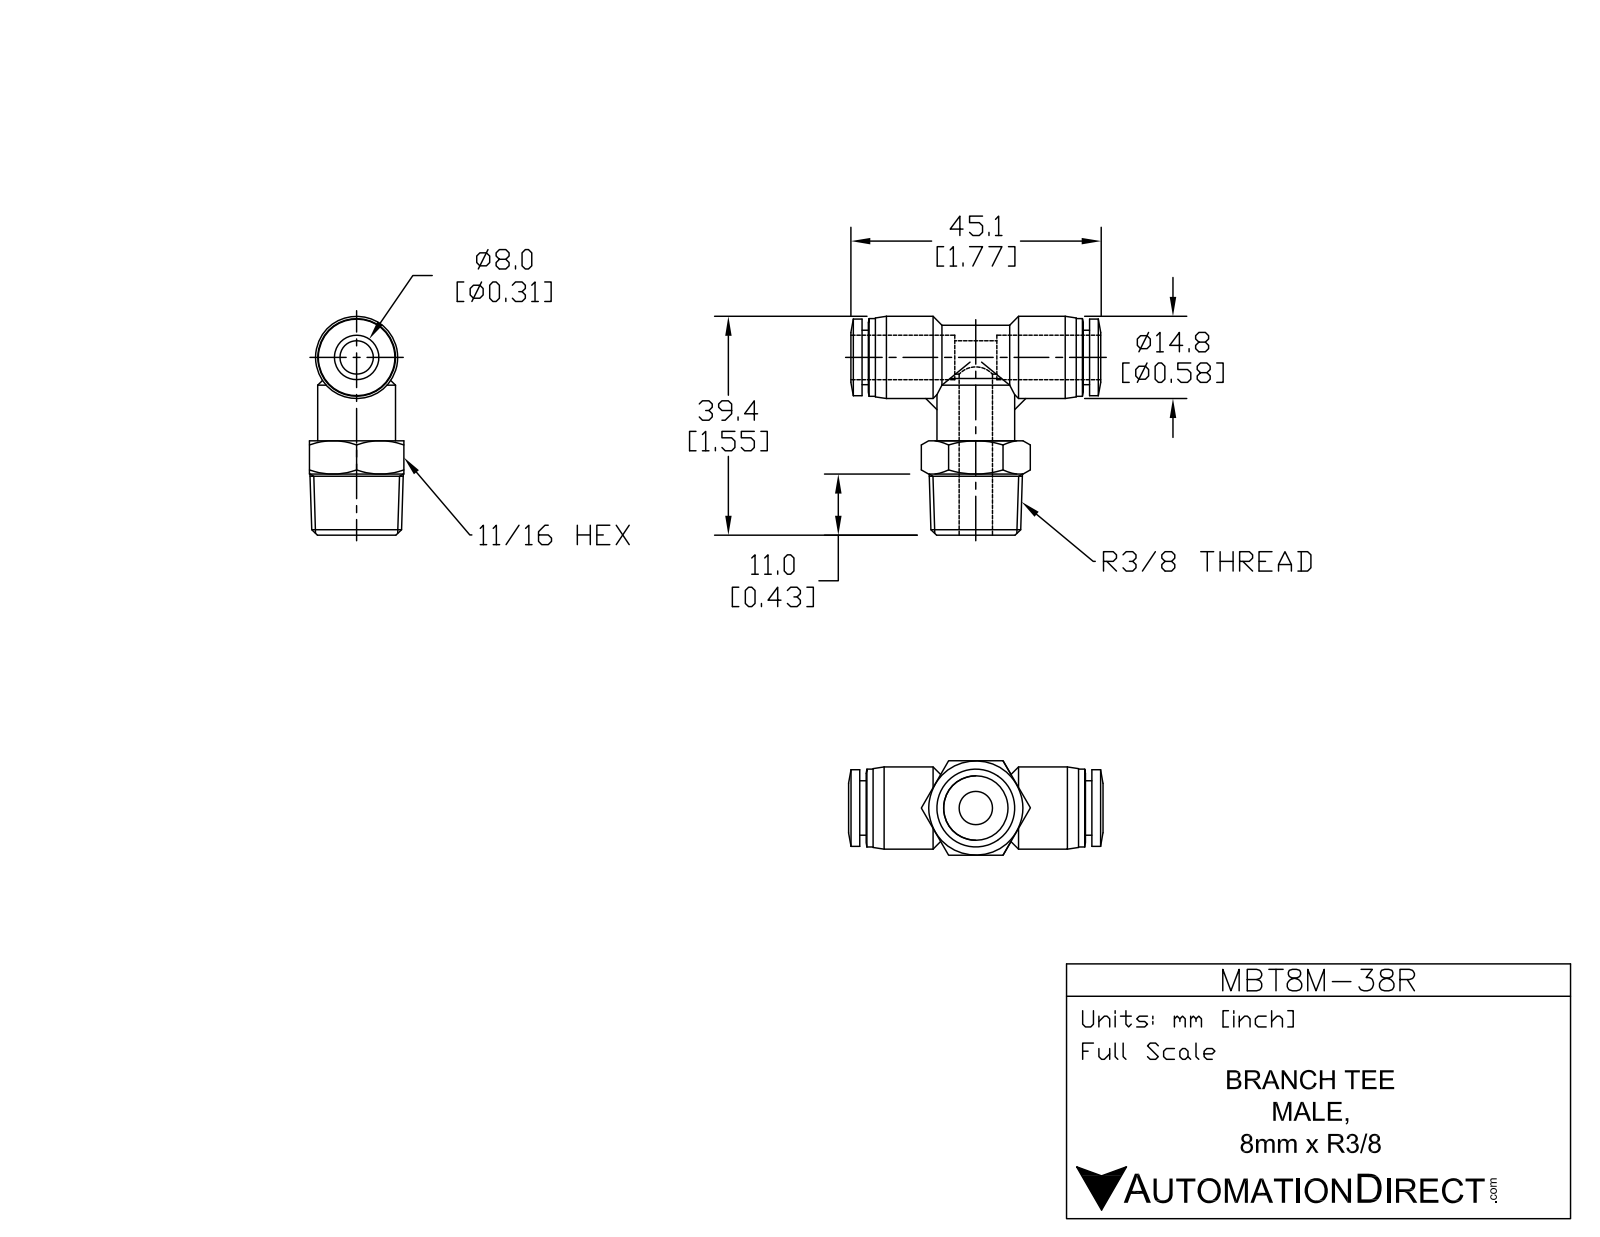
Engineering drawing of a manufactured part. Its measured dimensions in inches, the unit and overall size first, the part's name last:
Units: inches
Overall size (bounding box): 1.78 × 1.555 × 0.669
Round holes (diameter × count): ⌀0.236 ×2, ⌀0.327 ×1
Round bosses / shafts (diameter × count): ⌀0.591 ×1, ⌀0.559 ×1, ⌀0.551 ×1, ⌀0.543 ×1, ⌀0.457 ×1, ⌀0.386 ×1
Partial cylindrical surfaces — rounded edges, fillets, slot ends (radius × count): R0.228 ×1
Main face-to-face distances: 0.669, 0.045, 1.577, 1.622, 0.642, 0.98, 0.596, 0.935, 1.531, 0.339
Volume: 0.542 in³ · Surface area: 8.774 in²
Bodies: 1 solid, 100 faces (25 planar, 33 cylindrical, 42 other)
Part name (STEP PRODUCT): MBT8M-38R
STEP written by: SolidWorks 2015 (AUTOMOTIVE_DESIGN)
